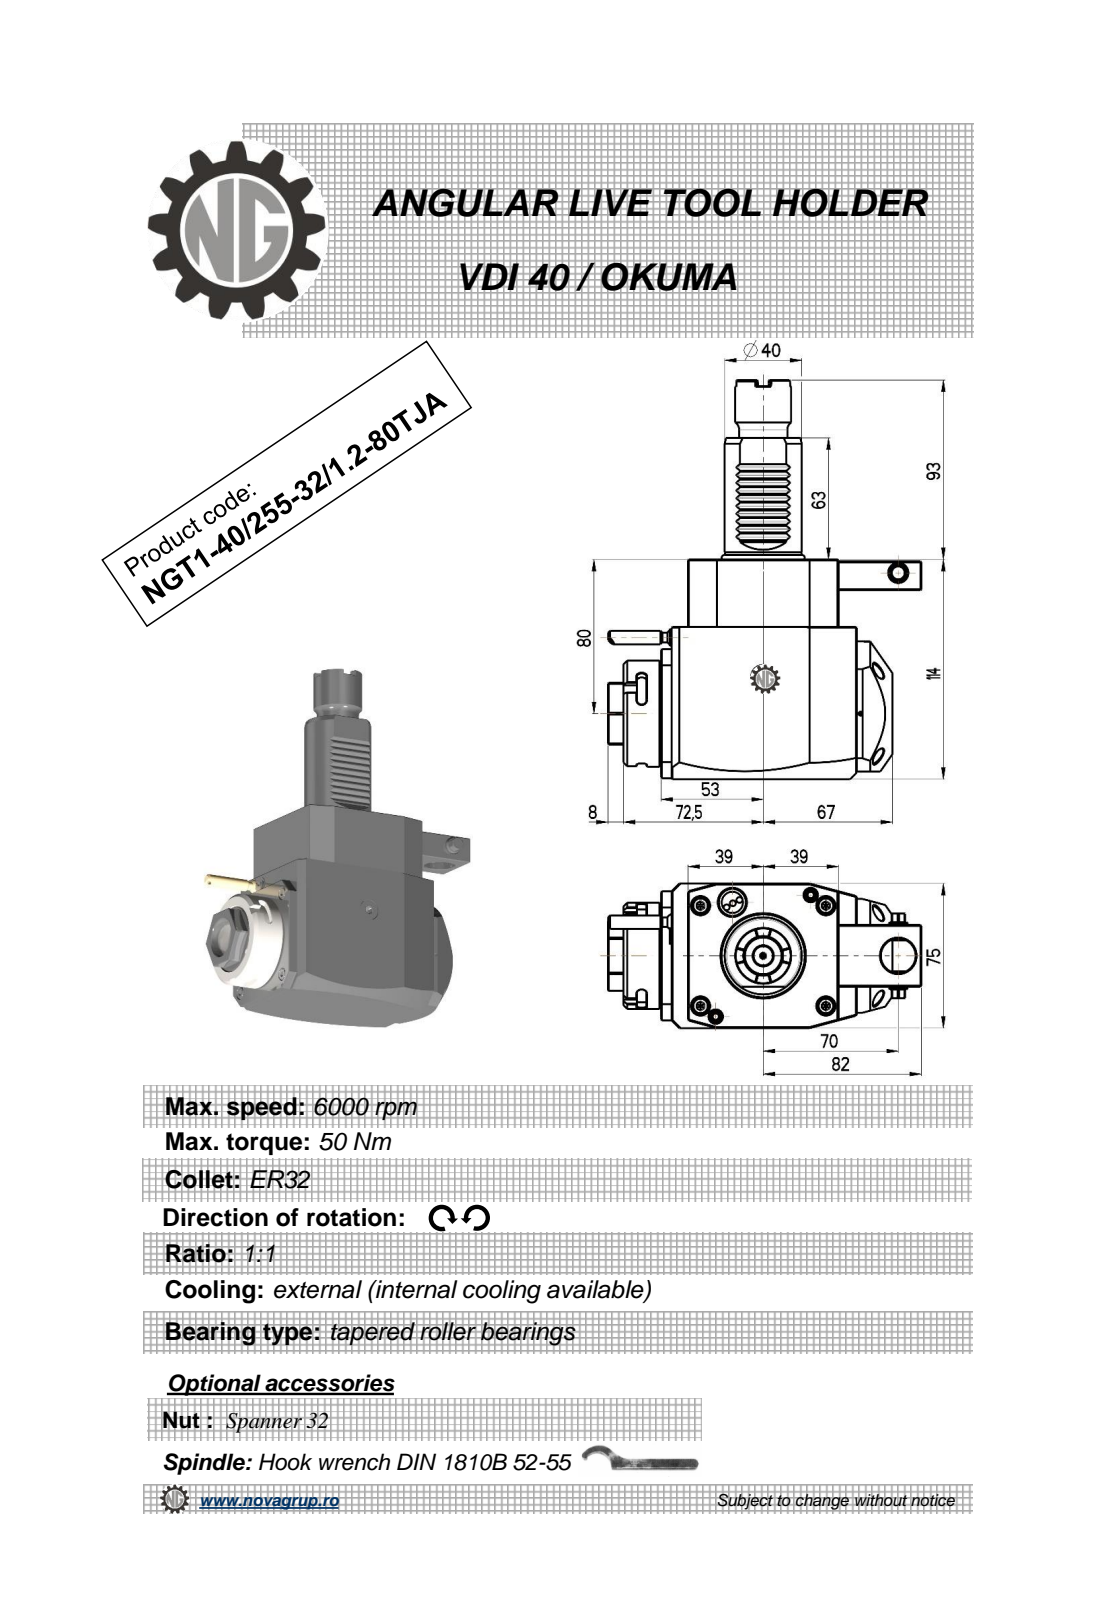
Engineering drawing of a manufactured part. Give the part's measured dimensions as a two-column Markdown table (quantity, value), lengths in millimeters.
| quantity | value |
| --- | --- |
| part name | NGT1_40_255_32_1_2_80TJA |
| STEP written by | PRO/ENGINEER BY PARAMETRIC TECHNOLOGY CORPORATION, 2010280 (CONFIG_CONTROL_DESIGN) |
| units | millimeters |
| bodies | 1 solid, 386 faces (202 planar, 78 cylindrical, 106 other) |
| overall size | 207 × 162.5 × 75 |
| volume | 986 670 mm³ |
| surface area | 76 048 mm² |
| round holes (diameter × count) | 2.5 × 1, 3 × 1, 9.5 × 1, 18 × 1, 23 × 1 |
| round bosses / shafts (diameter × count) | 8.96 × 2, 55 × 1, 48 × 1, 40 × 1, 29 × 1, 25 × 1, 10 × 1, 7 × 1 |
| partial cylindrical surfaces (radius × count) | 0.3 × 10, 2.5 × 6, 180 × 2, 0.5 × 1, 3.85 × 1, 4.25 × 1, 10 × 1, 24.5 × 1 |
| main face-to-face distances | 75, 114, 14, 33.5, 79, 92, 78, 21.5, 19.5, 111.5 |
| hole center spacings | 37.35, 43.2, 72.5 |
